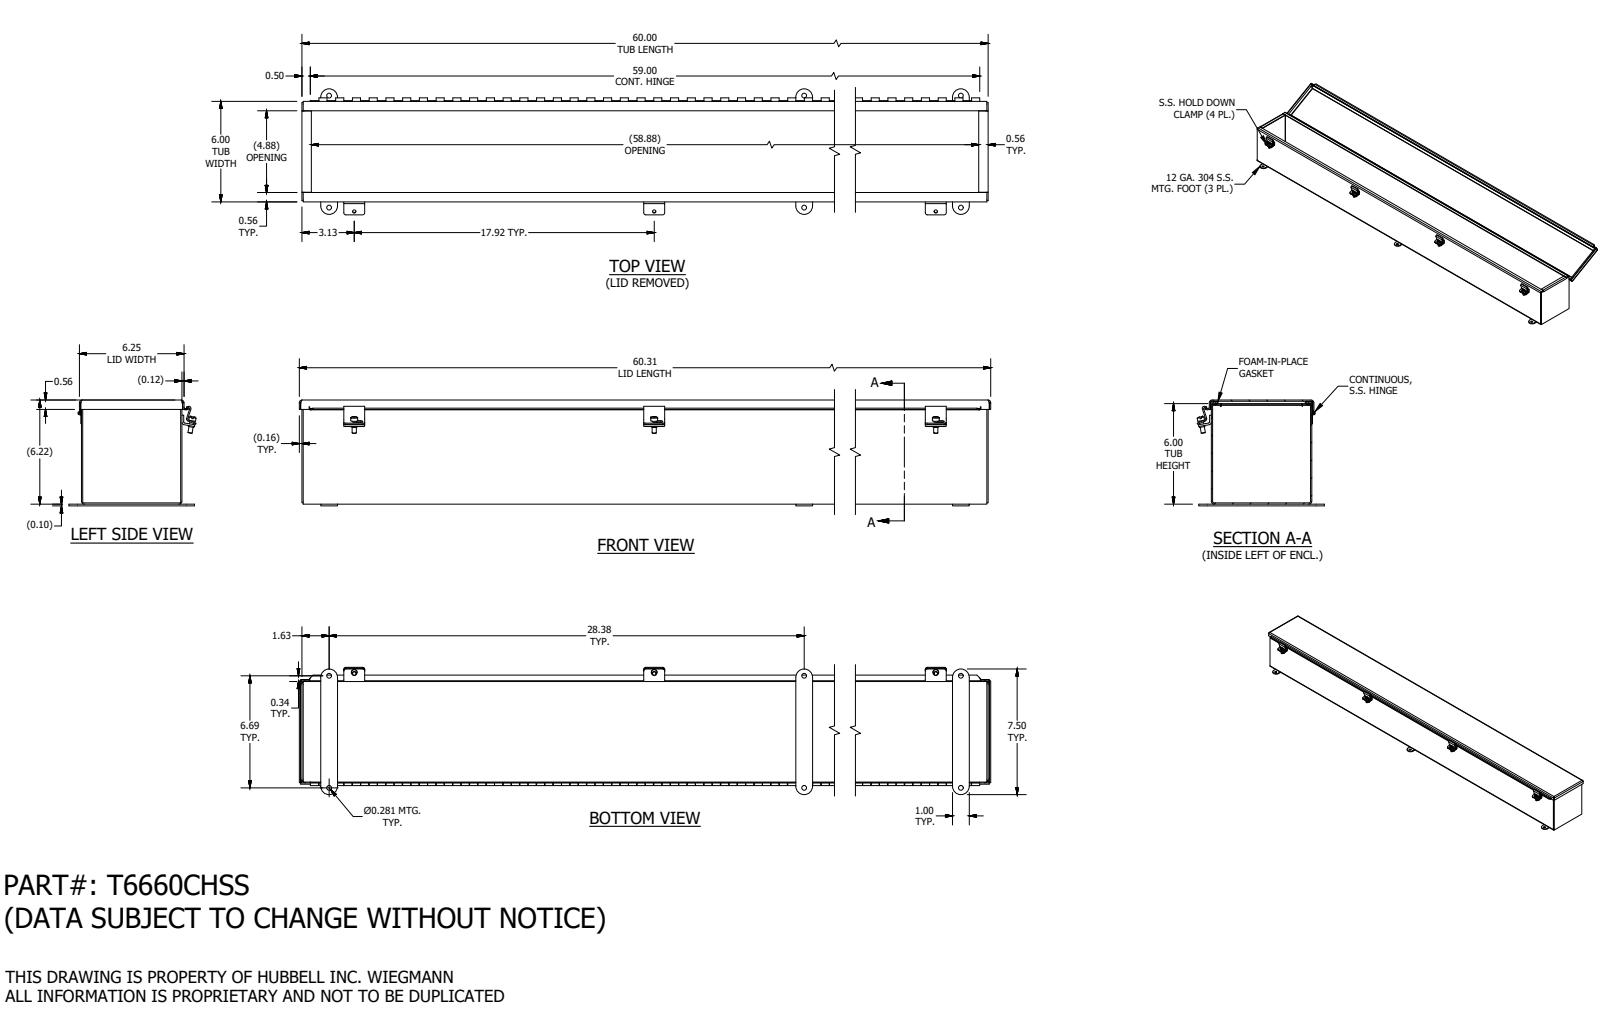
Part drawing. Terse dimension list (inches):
name: T6660CHSS
written by: SolidWorks 2019 (AUTOMOTIVE_DESIGN)
unit: in
bodies: 23 solids, 1024 faces (613 planar, 365 cylindrical, 46 other)
size: 60.313 × 7.598 × 6.322
volume: 140.5 in³; area: 3 750 in²
holes: 8× ⌀0.11, 6× ⌀0.281, 4× ⌀0.196, 1× ⌀0.116
bosses: 4× ⌀0.41, 4× ⌀0.344, 4× ⌀0.25, 1× ⌀0.2, 1× ⌀0.1
rounds: 16× R0.125, 11× R0.094, 11× R0.168, 8× R0.085, 8× R0.133, 6× R0.5, 4× R0.242, 3× R0.063
face distances: 0.074, 5.926, 6.144, 6, 5.852, 6.218, 6.07, 0.218, 6.052, 0.126
hole spacings: 17.917, 0.75, 28.375, 29.152, 35.833, 6.687, 17.167, 17.917
